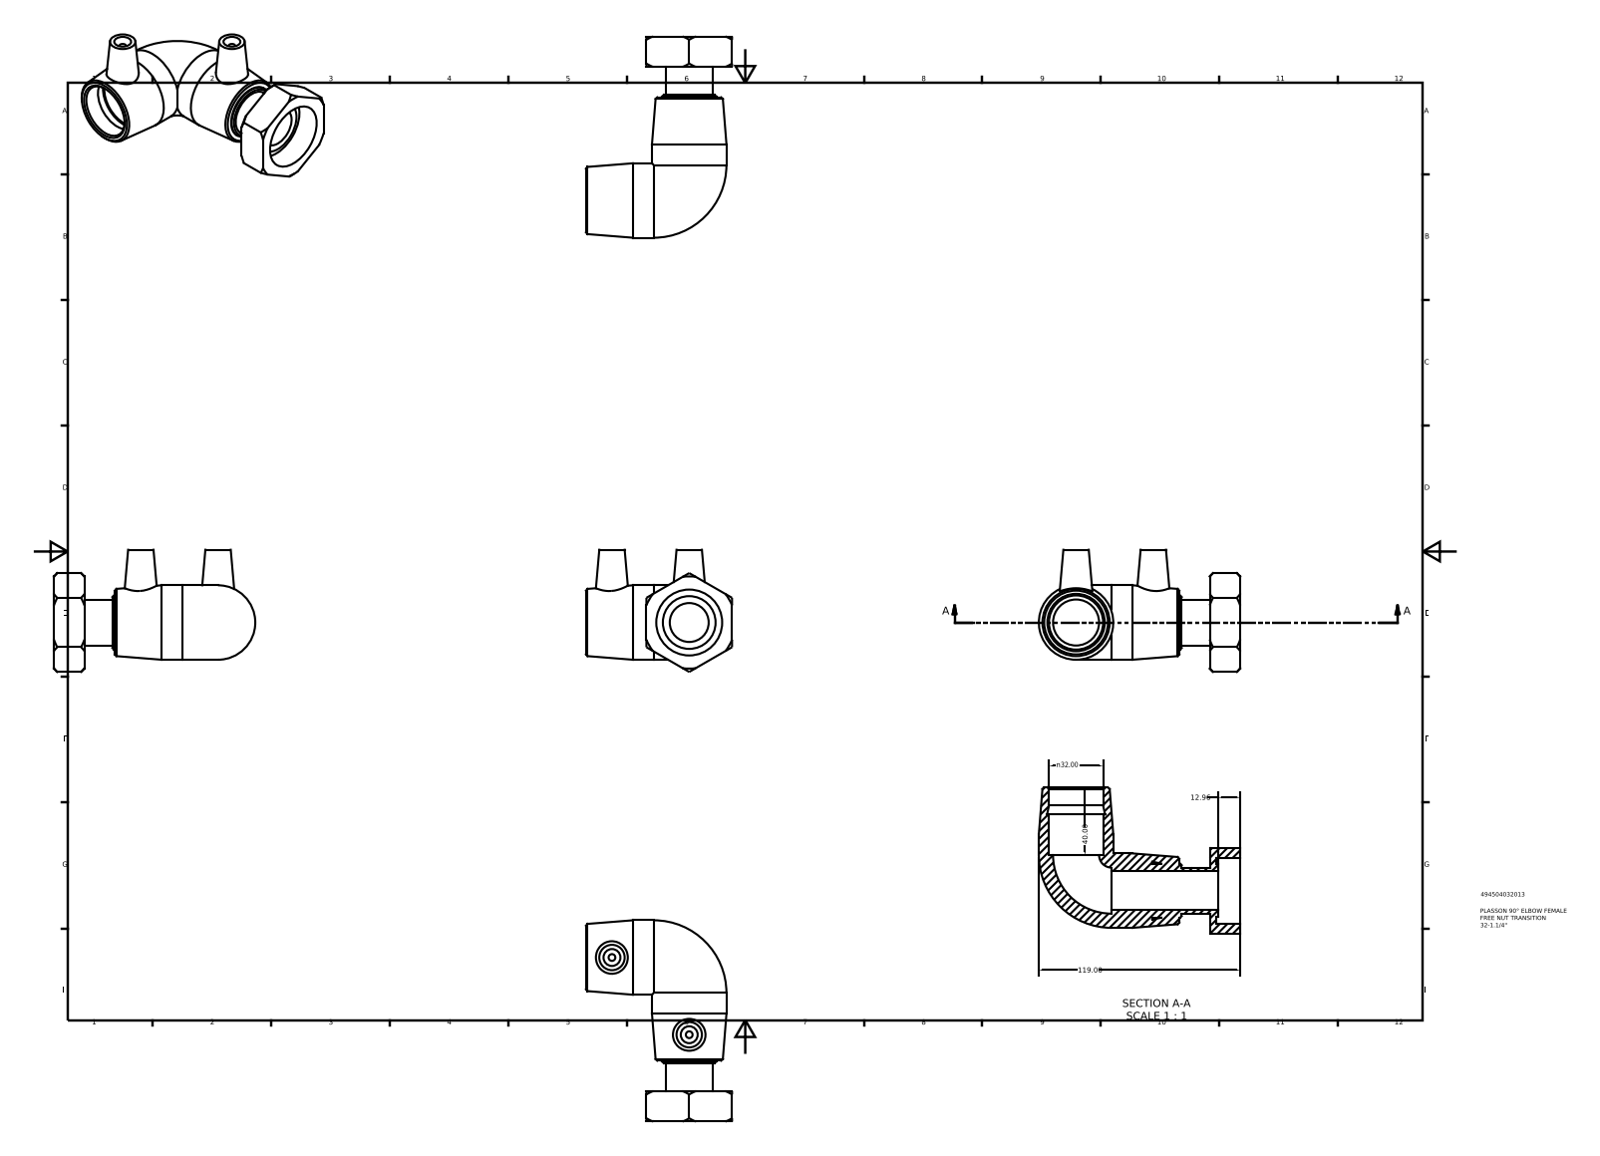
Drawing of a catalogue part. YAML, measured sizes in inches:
part_name: "494504032013"
step_written_by: "Autodesk Inventor 2015 (AUTOMOTIVE_DESIGN)"
units: inches
bodies: {solids: 1, faces: 61, planar: 23, cylindrical: 14, other: 24}
overall_size: [4.685, 3.398, 2.843]
volume: 7.914
surface_area: 66.11
round_holes:
  - {diameter: 0.394, count: 2}
  - {diameter: 0.906, count: 1}
  - {diameter: 1.26, count: 1}
  - {diameter: 1.533, count: 1}
round_bosses_or_shafts:
  - {diameter: 1.732, count: 2}
  - {diameter: 0.157, count: 2}
  - {diameter: 1.26, count: 1}
  - {diameter: 1.227, count: 1}
  - {diameter: 1.074, count: 1}
face_to_face_distances: [1.992, 0.709, 0.057, 0.85, 0.142, 0.567, 1.575, 0.198, 0.51, 0.907]
hole_center_spacings: [2.542]
